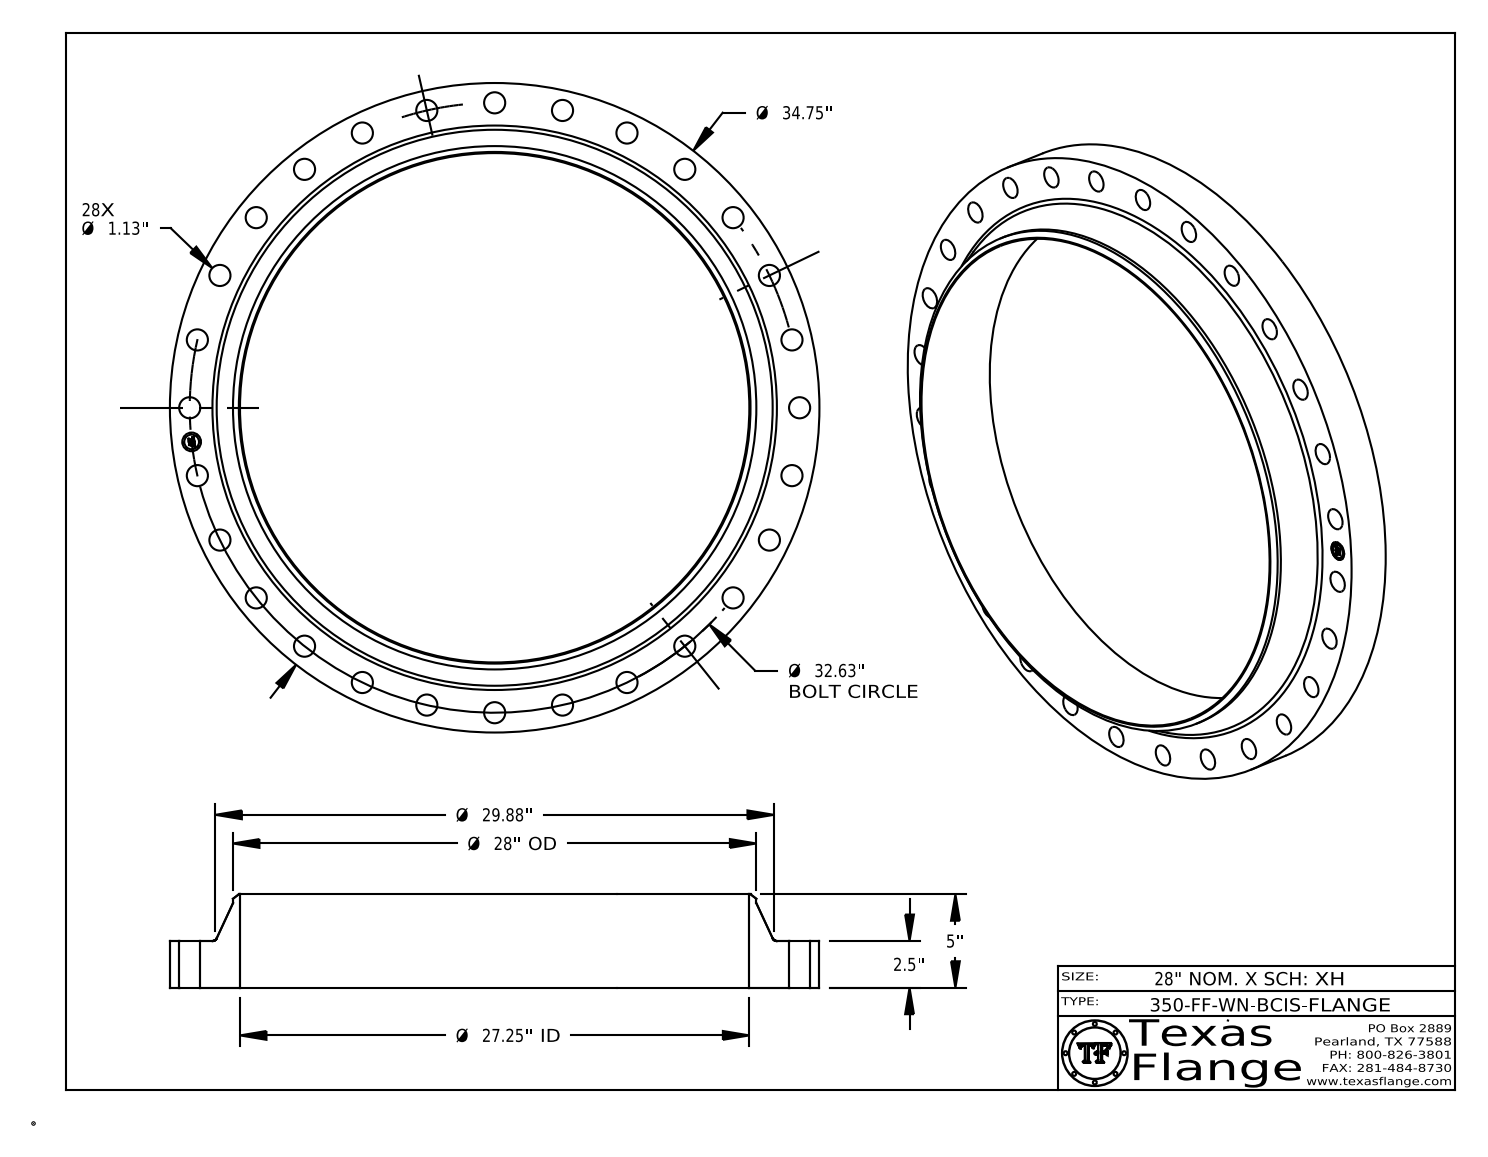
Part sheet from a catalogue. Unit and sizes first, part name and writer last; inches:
Units: inches
Overall size (bounding box): 34.75 × 34.75 × 5
Round holes (diameter × count): ⌀1.13 ×28, ⌀1 ×1, ⌀27.25 ×1
Round bosses / shafts (diameter × count): ⌀0.061 ×8, ⌀34.75 ×1, ⌀28 ×1, ⌀0.788 ×1
Main face-to-face distances: 2.5, 5, 0.015, 2.485, 2.515, 0.298, 0.293, 0.054, 0.193, 0.248
Hole centre spacings: 14.157, 16.315, 23.073, 25.511, 27.628, 29.398, 20.344, 7.261
Volume: 1 007 in³ · Surface area: 1 766 in²
Bodies: 1 solid, 456 faces (368 planar, 82 cylindrical, 6 other)
Part name (STEP PRODUCT): 350-FF-WN, BCIS
STEP written by: CATIA V5 STEP AP214 (AUTOMOTIVE_DESIGN)
